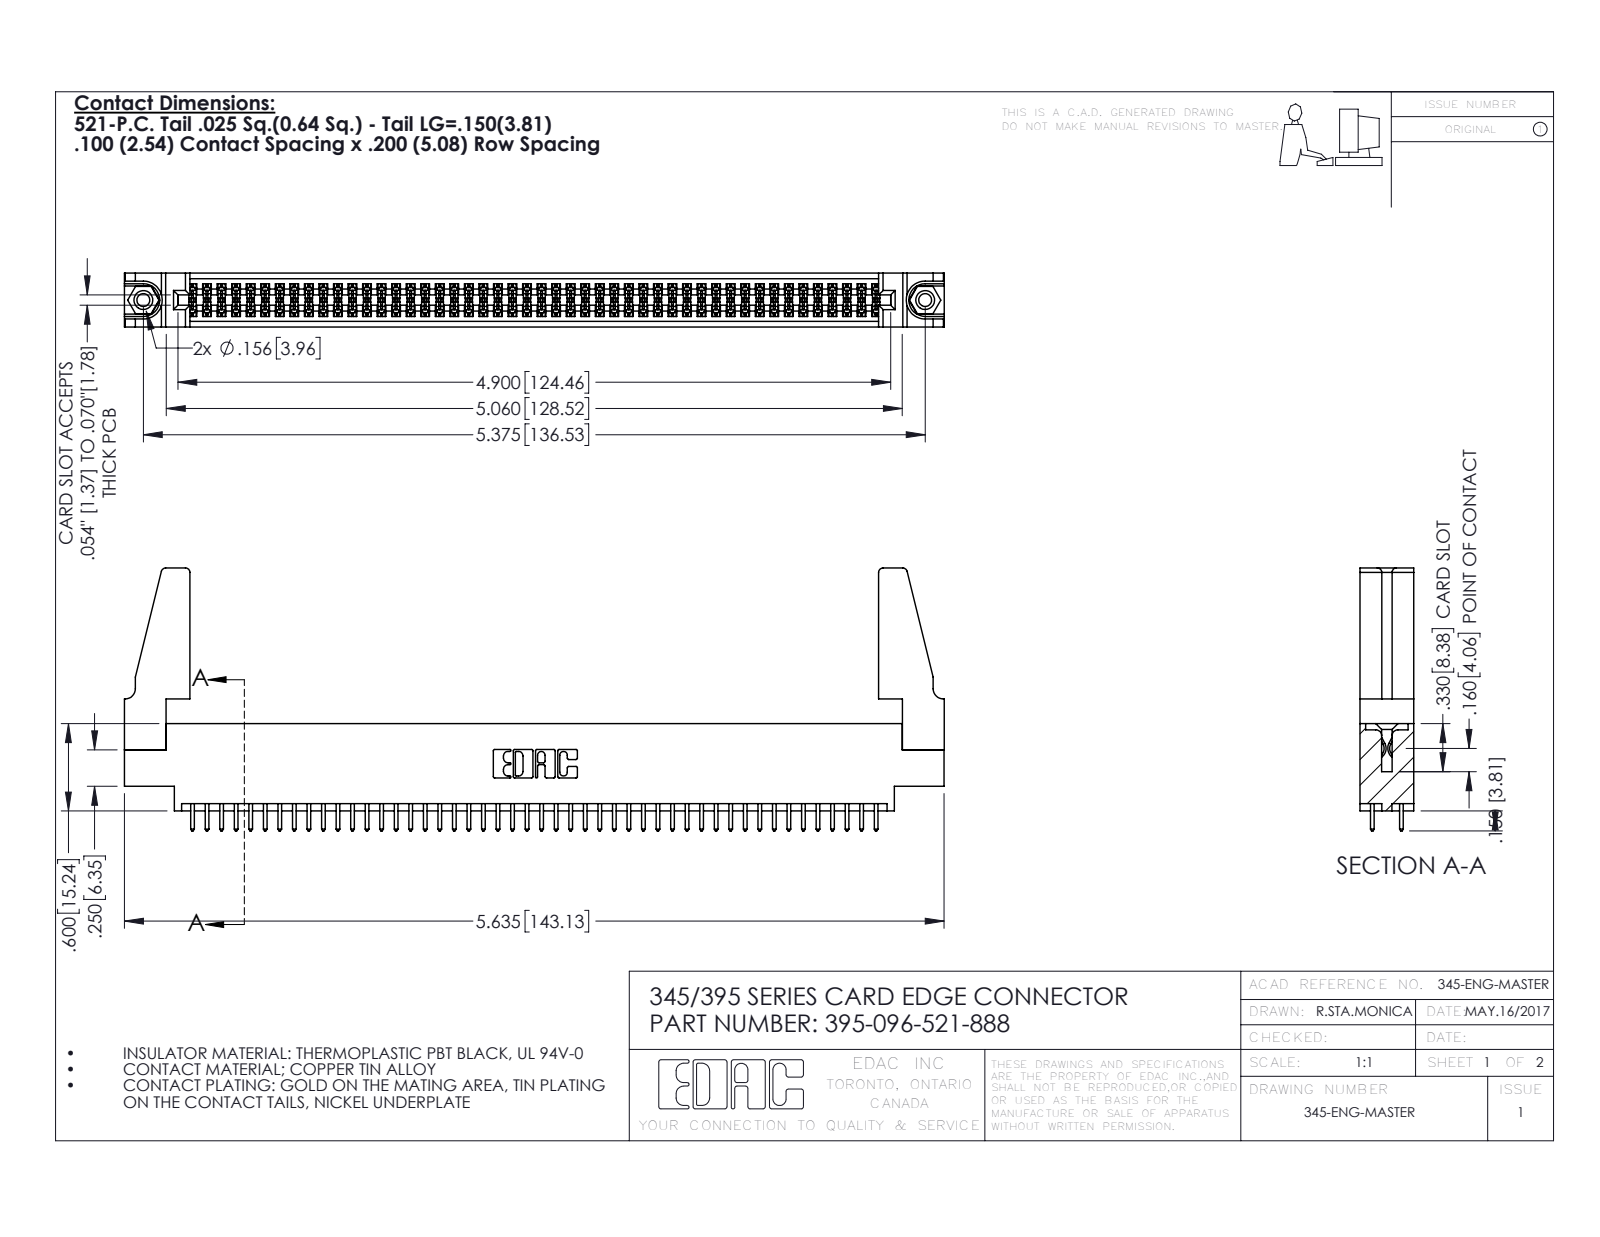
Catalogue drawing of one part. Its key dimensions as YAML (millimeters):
part_name: "395-096-521-888; 345 Part_0.170 Offset - 0.156 Dia-TH; 345-292-001_345-293-121; 345-250-001_345-250-001-102 (+1 more)"
step_written_by: "SolidWorks 2016 (CONFIG_CONTROL_DESIGN)"
units: millimeters
bodies: {solids: 101, faces: 5054, planar: 3324, cylindrical: 1714, other: 16}
overall_size: [143.2, 45.9, 9.4]
volume: 17060
surface_area: 23540
round_holes:
  - {diameter: 2.3, count: 2}
  - {diameter: 3.2, count: 2}
  - {diameter: 4, count: 2}
  - {diameter: 1.6, count: 1}
round_bosses_or_shafts:
  - {diameter: 3.9, count: 2}
partial_cylinders:
  - {radius: 0.2, count: 144}
  - {radius: 0.3, count: 96}
  - {radius: 0.3, count: 22}
  - {radius: 0.8, count: 8}
  - {radius: 0.2, count: 6}
  - {radius: 0.8, count: 6}
  - {radius: 0.7, count: 3}
  - {radius: 0.4, count: 2}
face_to_face_distances: [1.8, 7.6, 9.4, 2.5, 6.9, 0.6, 5.1, 5.7, 4.4, 3.8]
hole_center_spacings: [6.9, 130.5, 136.5]
